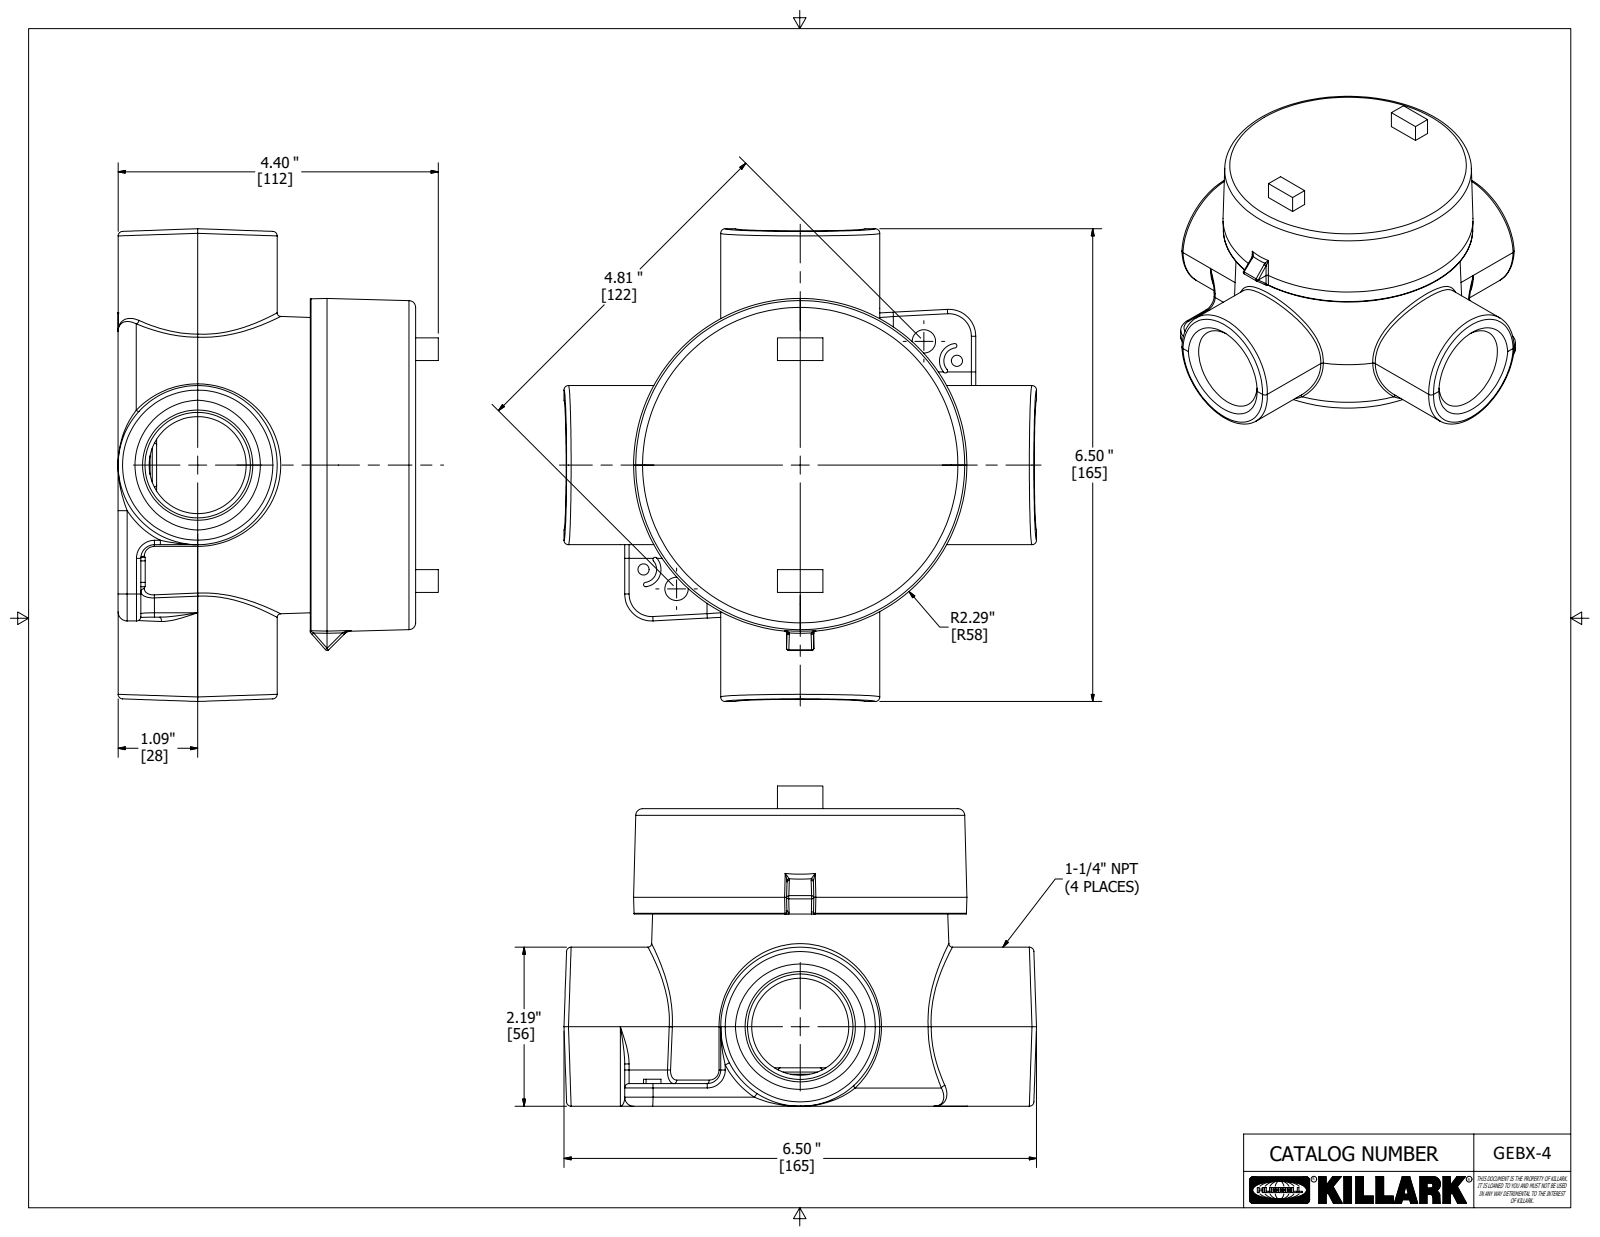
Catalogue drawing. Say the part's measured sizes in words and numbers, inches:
The part is named "GEBX-4; 21153; 21147-override". Its 3-D file was written by "Autodesk Inventor 2020 (AUTOMOTIVE_DESIGN)". It is 2 solids with 889 faces: 426 planar, 99 cylindrical and 364 other. Overall it measures 6.5 by 6.5 by 4.405 inches. Its volume is 39.31 cubic inches and its surface area 225.8 square inches. Round holes: 2 of diameter 0.153, 2 of diameter 0.321, 2 of diameter 1.334, 1 of diameter 3.823, 1 of diameter 4.045. Round bosses or shafts: 2 of diameter 2.188. Partial cylindrical surfaces (rounded edges, fillets, slot ends): 36 of radius 0.06, 14 of radius 0.03, 4 of radius 0.125, 4 of radius 0.187, 3 of radius 0.031, 2 of radius 0.18, 2 of radius 0.24, 2 of radius 0.37. The main face-to-face distances are 4.093, 3.655, 0.437, 3.5, 0.155, 0.593, 2.644, 0.856, 1.011, 1.449. The hole center spacings are 0.527, 2.406, 2.589, 4.97, 4.812, 5.178.
